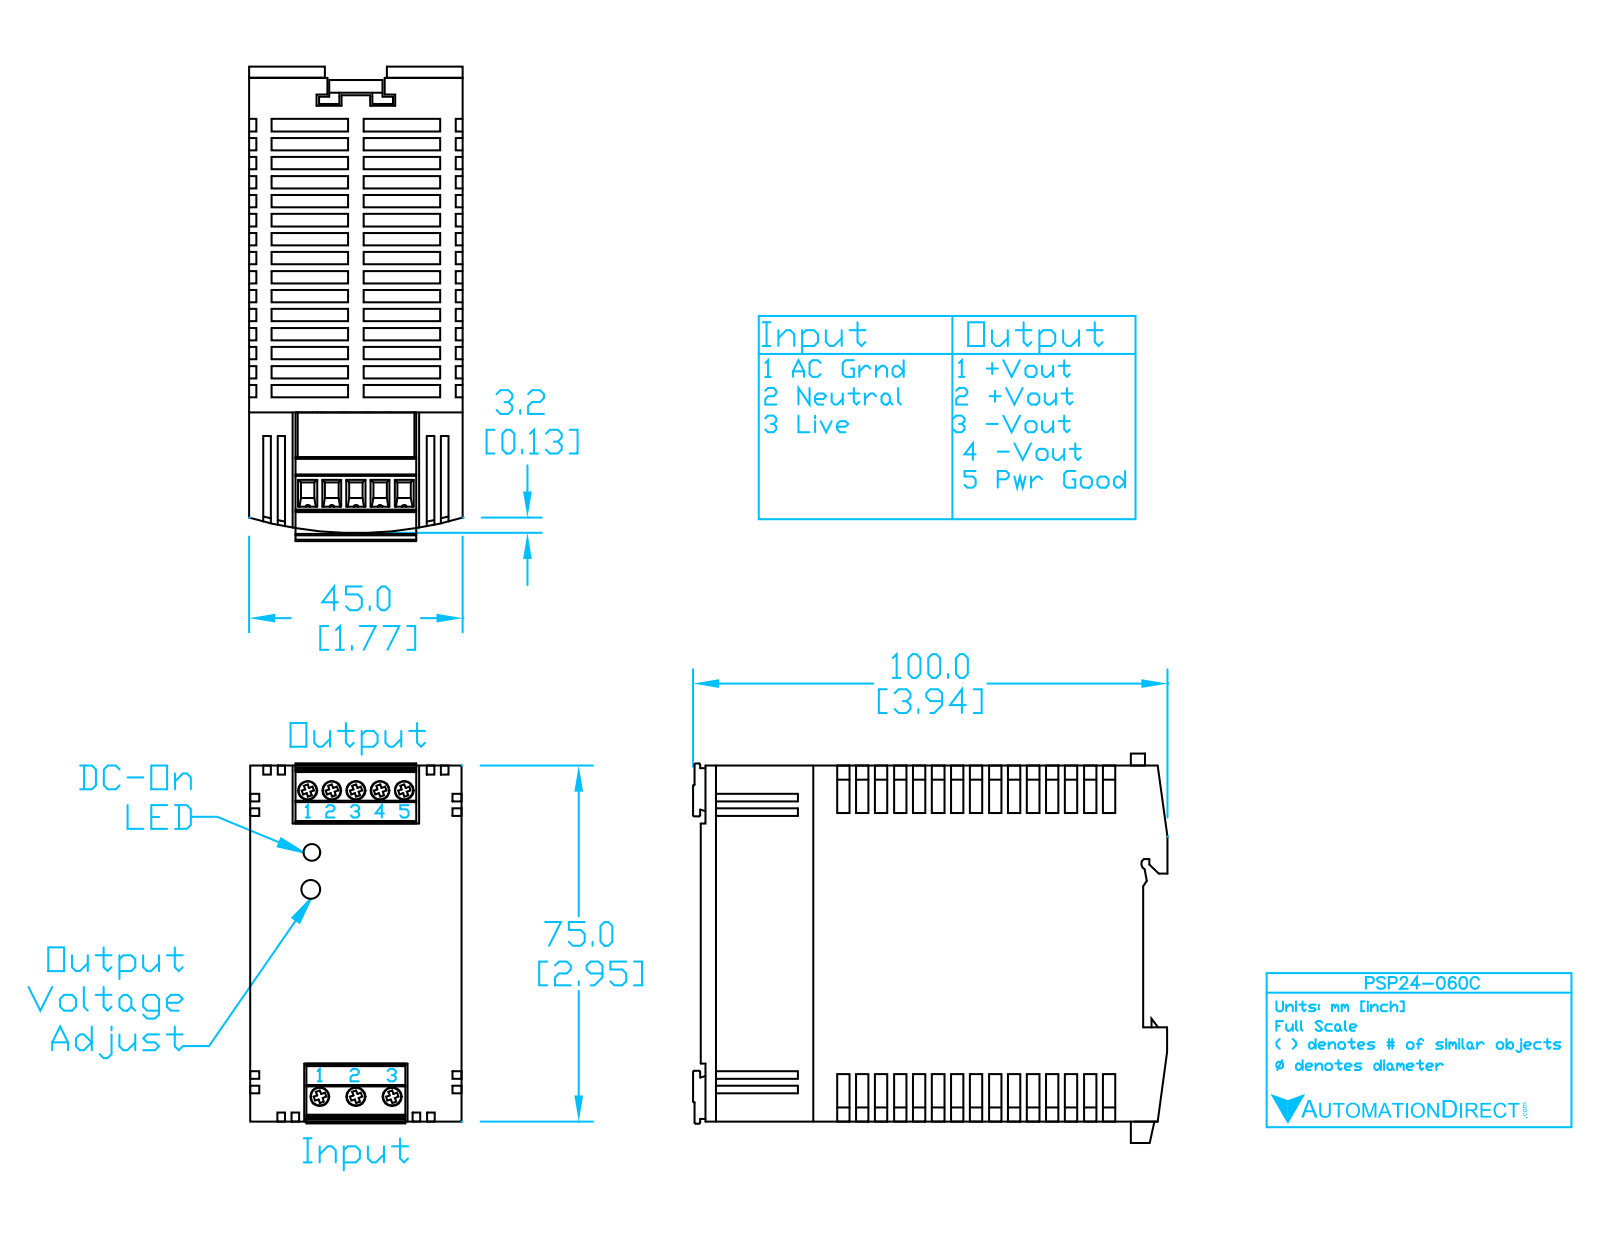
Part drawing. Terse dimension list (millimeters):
name: PSP24-060C
written by: SolidWorks 2011 (CONFIG_CONTROL_DESIGN)
unit: mm
bodies: 3 solids, 485 faces (414 planar, 0 cylindrical, 71 other)
size: 100.29 × 80 × 45
volume: 319 905 mm³; area: 39 714 mm²
face distances: 45, 75, 12.25, 62.75, 2, 1.7, 50.5, 2.09, 16, 70.85
